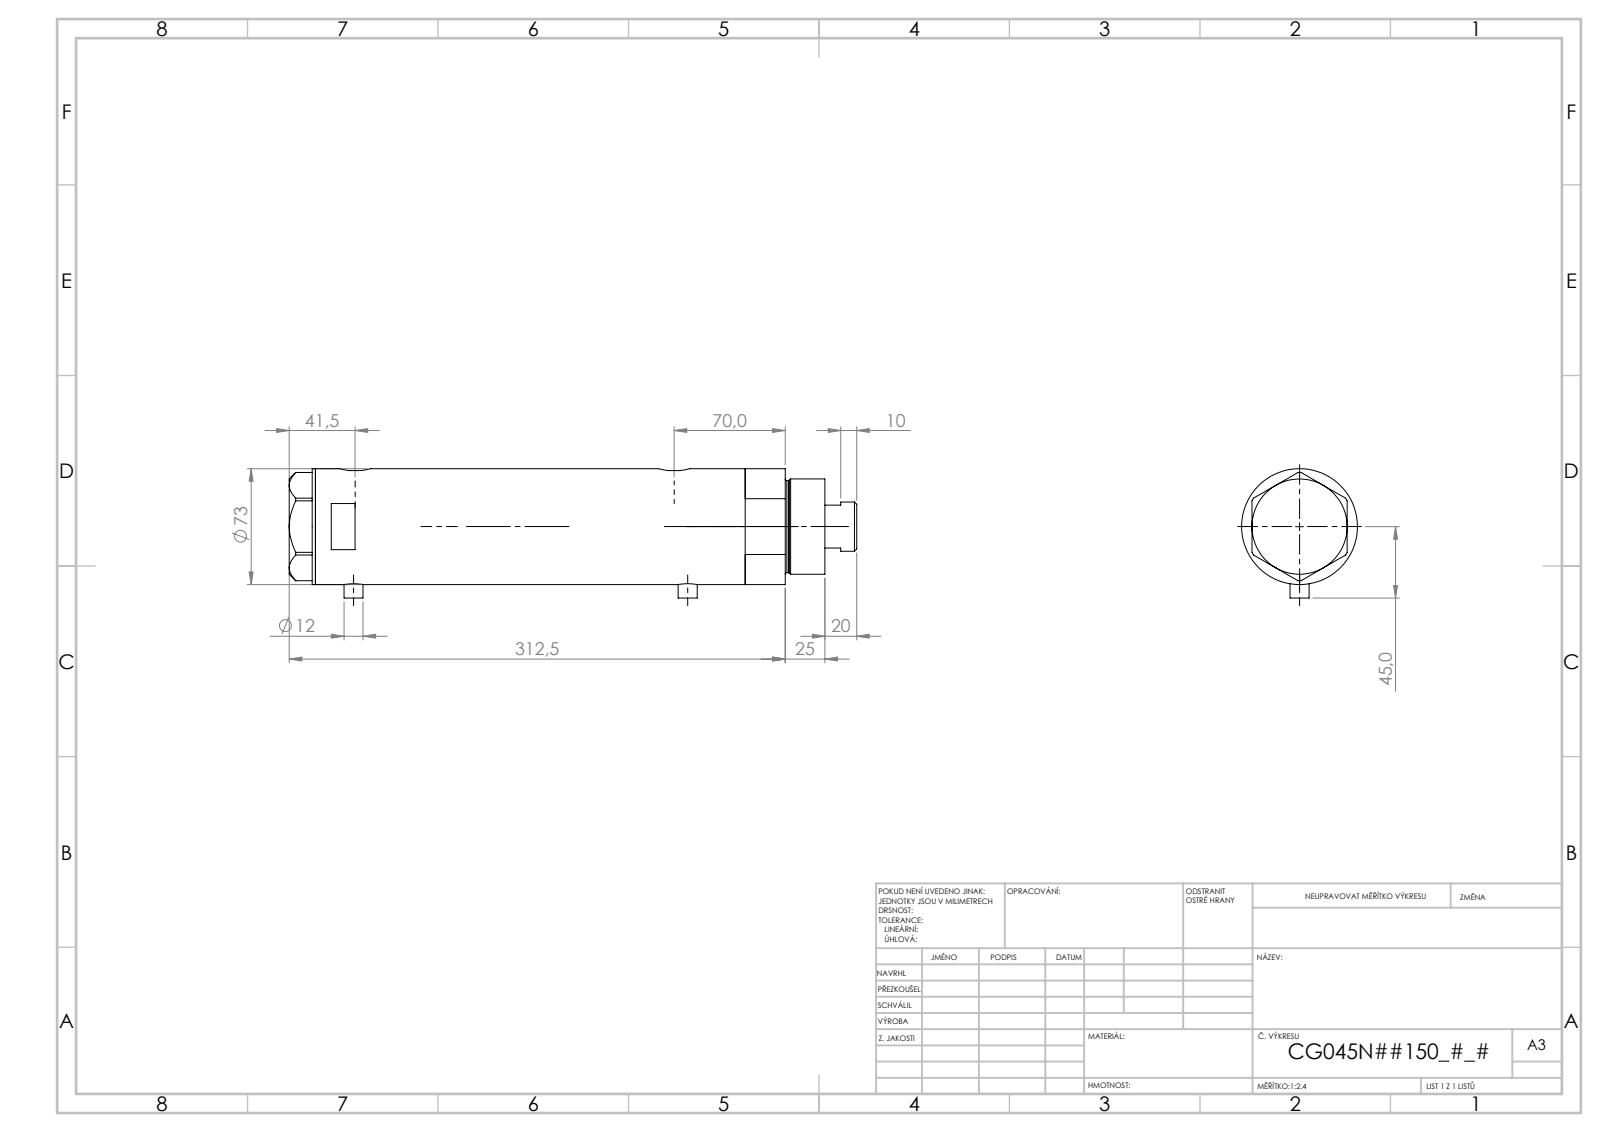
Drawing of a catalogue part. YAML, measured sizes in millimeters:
part_name: "V270CG_FRONT; V270CG_BACK; V270CG_VC; V270CG_MIDDLE"
step_written_by: "SolidWorks 2019 (CONFIG_CONTROL_DESIGN)"
units: millimeters
bodies: {solids: 4, faces: 132, planar: 63, cylindrical: 49, other: 20}
overall_size: [184.4, 53.1, 52]
volume: 275729
surface_area: 82127
round_holes:
  - {diameter: 5, count: 2}
  - {diameter: 9.64, count: 2}
  - {diameter: 12.5, count: 2}
  - {diameter: 15, count: 2}
  - {diameter: 6.5, count: 1}
  - {diameter: 20, count: 1}
  - {diameter: 21.5, count: 1}
  - {diameter: 45, count: 1}
round_bosses_or_shafts:
  - {diameter: 12, count: 2}
  - {diameter: 52, count: 1}
  - {diameter: 44, count: 1}
  - {diameter: 40, count: 1}
  - {diameter: 38, count: 1}
  - {diameter: 33, count: 1}
  - {diameter: 19, count: 1}
face_to_face_distances: [23.8, 9, 32.8, 62.55, 53.55, 29.75, 102.5, 93.5, 69.7, 39.95]
hole_center_spacings: [2.9, 4.5, 66.7, 69.6, 71.2, 74.1]
